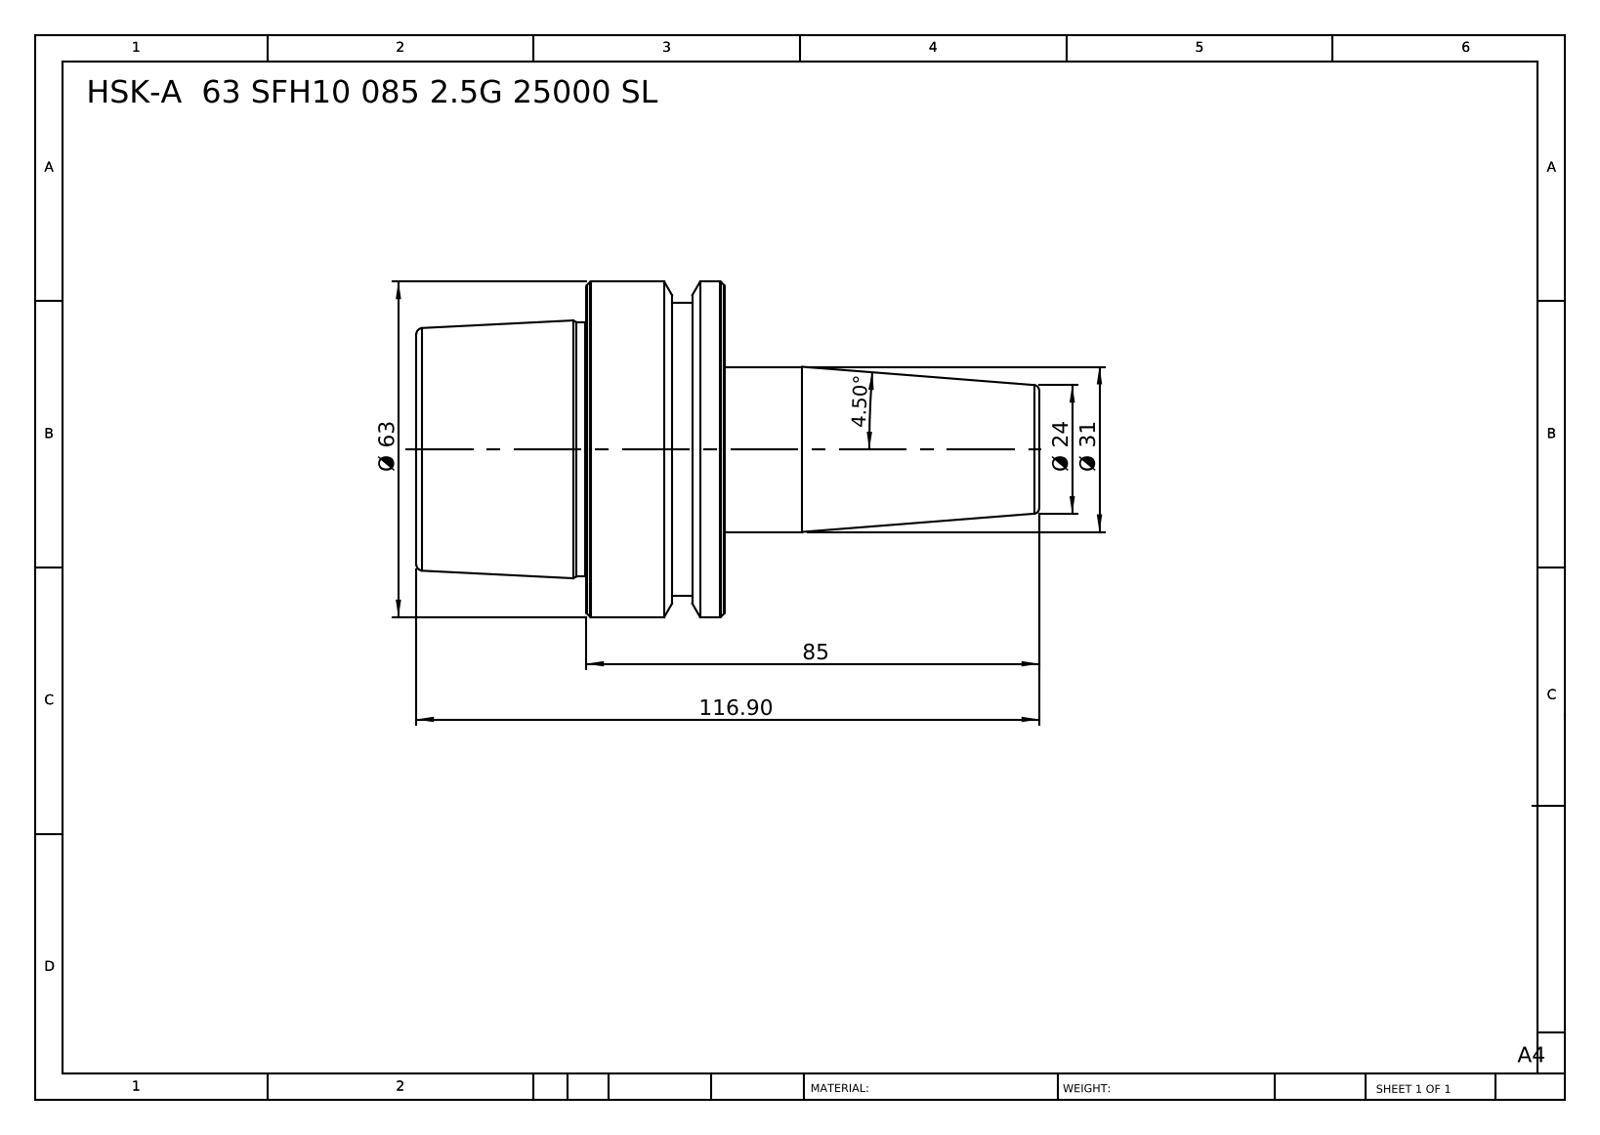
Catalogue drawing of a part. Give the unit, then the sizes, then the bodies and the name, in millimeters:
Units: millimetres
Overall size (bounding box): 116.9 × 63 × 63
Round bosses / shafts (diameter × count): ⌀63 ×1, ⌀55 ×1, ⌀47.78 ×1, ⌀31 ×1
Main face-to-face distances: 57.9, 26, 31.9, 59, 85, 116.9, 65.1, 6.1, 19.9, 51.8
Volume: 170 105 mm³ · Surface area: 21 588 mm²
Bodies: 1 solid, 46 faces (6 planar, 10 cylindrical, 30 other)
Part name (STEP PRODUCT): HSK-A 63 SFH10 080 2.5G 25000 SL
STEP written by: SolidWorks 2014 (CONFIG_CONTROL_DESIGN)
